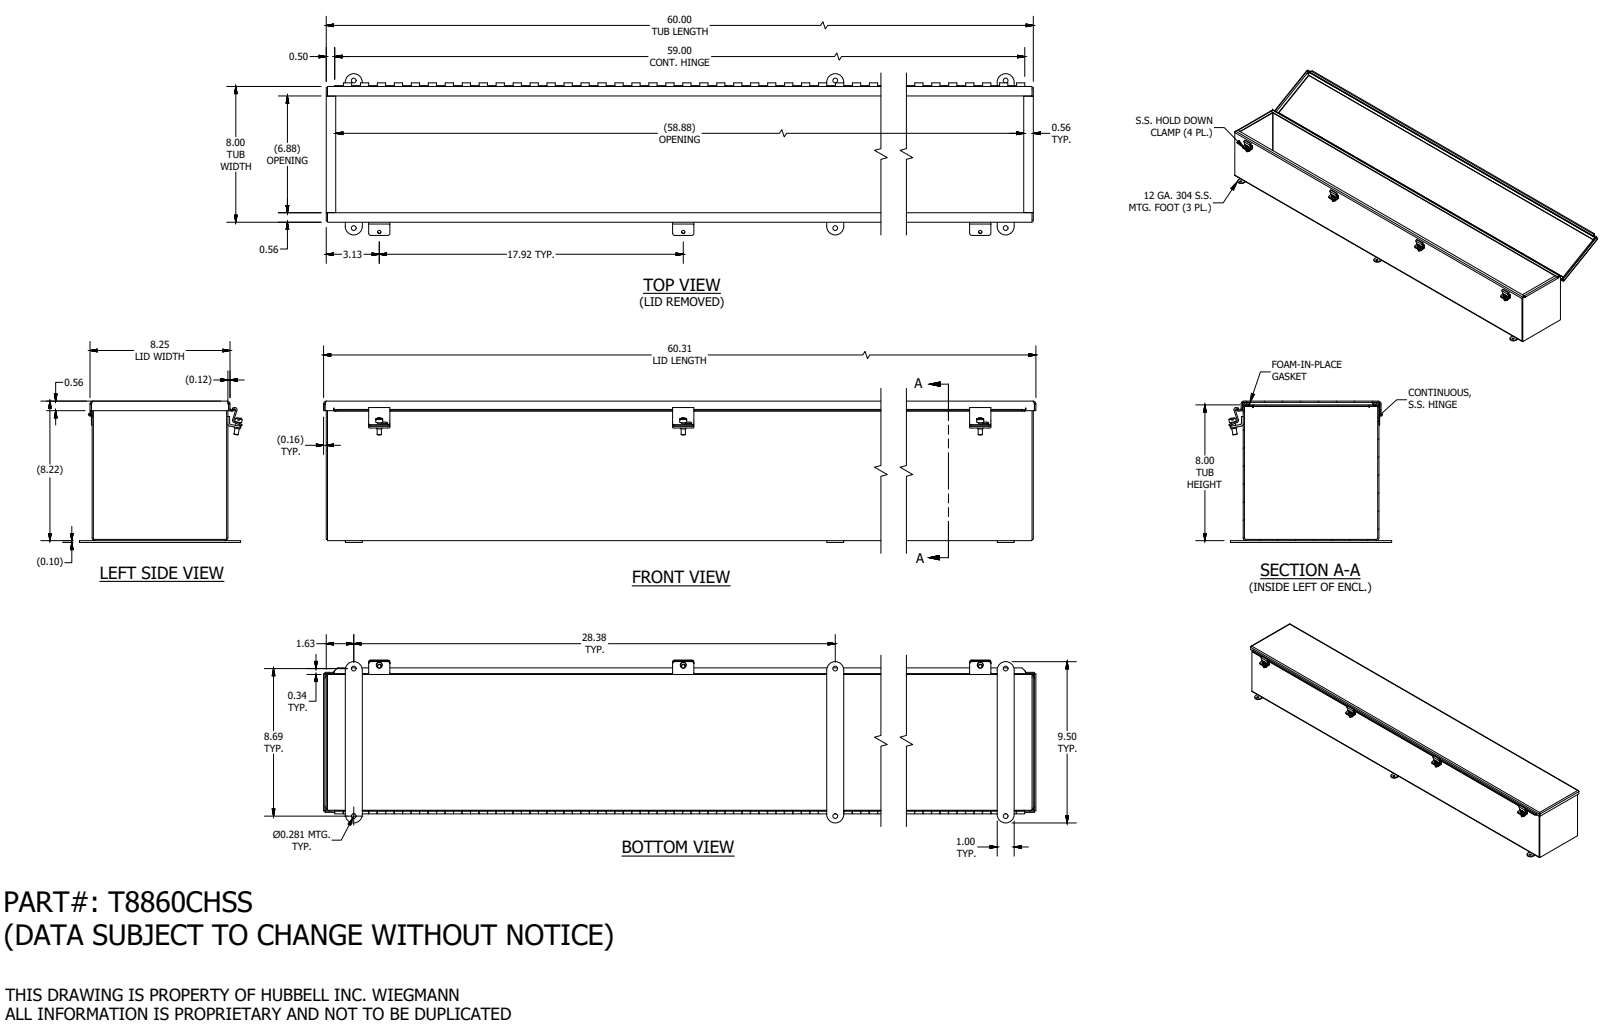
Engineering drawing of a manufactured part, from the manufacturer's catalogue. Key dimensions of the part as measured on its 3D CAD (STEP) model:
Part name (STEP PRODUCT): T8860CHSS
STEP written by: SolidWorks 2019 (AUTOMOTIVE_DESIGN)
Units: inches
Bodies: 23 solids, 1024 faces (613 planar, 365 cylindrical, 46 other)
Overall size (bounding box): 60.313 × 9.598 × 8.322
Volume: 181.3 in³ · Surface area: 4 846 in²
Round holes (diameter × count): ⌀0.11 ×8, ⌀0.281 ×6, ⌀0.196 ×4, ⌀0.116 ×1
Round bosses / shafts (diameter × count): ⌀0.41 ×4, ⌀0.344 ×4, ⌀0.25 ×4, ⌀0.2 ×1, ⌀0.1 ×1
Partial cylindrical surfaces — rounded edges, fillets, slot ends (radius × count): R0.125 ×16, R0.094 ×11, R0.168 ×11, R0.085 ×8, R0.133 ×8, R0.5 ×6, R0.242 ×4, R0.063 ×3
Main face-to-face distances: 0.074, 7.926, 8.144, 8, 7.852, 8.218, 8.07, 59.926, 0.218, 8.052
Hole centre spacings: 17.917, 0.75, 28.375, 29.675, 35.833, 8.687, 17.167, 17.917
